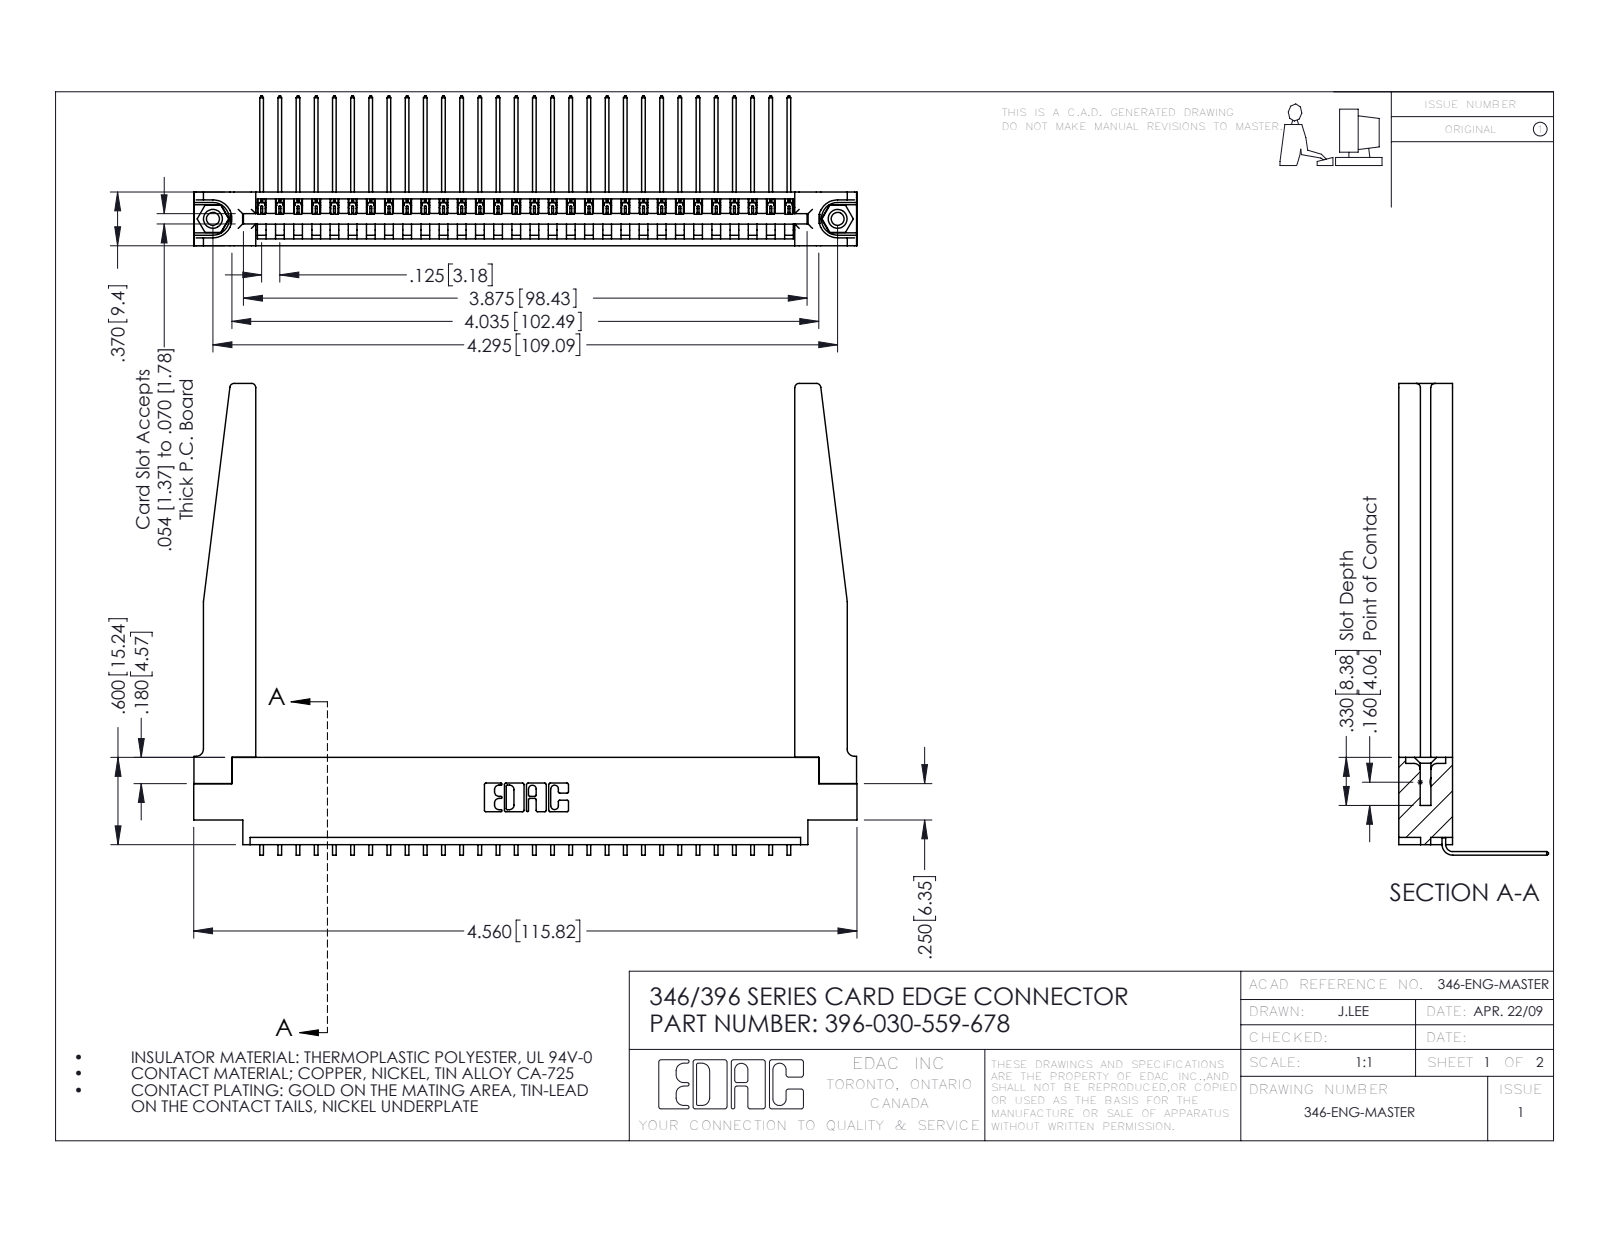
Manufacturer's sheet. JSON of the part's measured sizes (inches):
{"part_name": "345-292-001_558 559 Tail - 1; 345-250-001_345-250-001-102; 346-220-078_345-220-078; 346 Part_0.170 Offset - 0.156 Dia-TH (+1 more)", "step_written_by": "SolidWorks 2016 (CONFIG_CONTROL_DESIGN)", "units": "inches", "bodies": {"solids": 35, "faces": 2160, "planar": 1482, "cylindrical": 626, "other": 52}, "overall_size": [4.56, 3.243, 1.03], "volume_in3": 1.09, "surface_area_in2": 32.32, "round_holes": [[0.089, 2], [0.125, 2], [0.156, 2], [0.064, 1]], "round_bosses_or_shafts": [[0.155, 2]], "partial_cylinders_radius": [[0.006, 60], [0.01, 22], [0.03, 8], [0.007, 6], [0.031, 6], [0.026, 3], [0.05, 3], [0.031, 2]], "face_to_face_distances": [0.37, 0.048, 0.322, 0.072, 0.148, 0.15, 0.025, 0.25, 0.298, 0.222], "hole_center_spacings": [0.246, 4.087, 4.295]}
